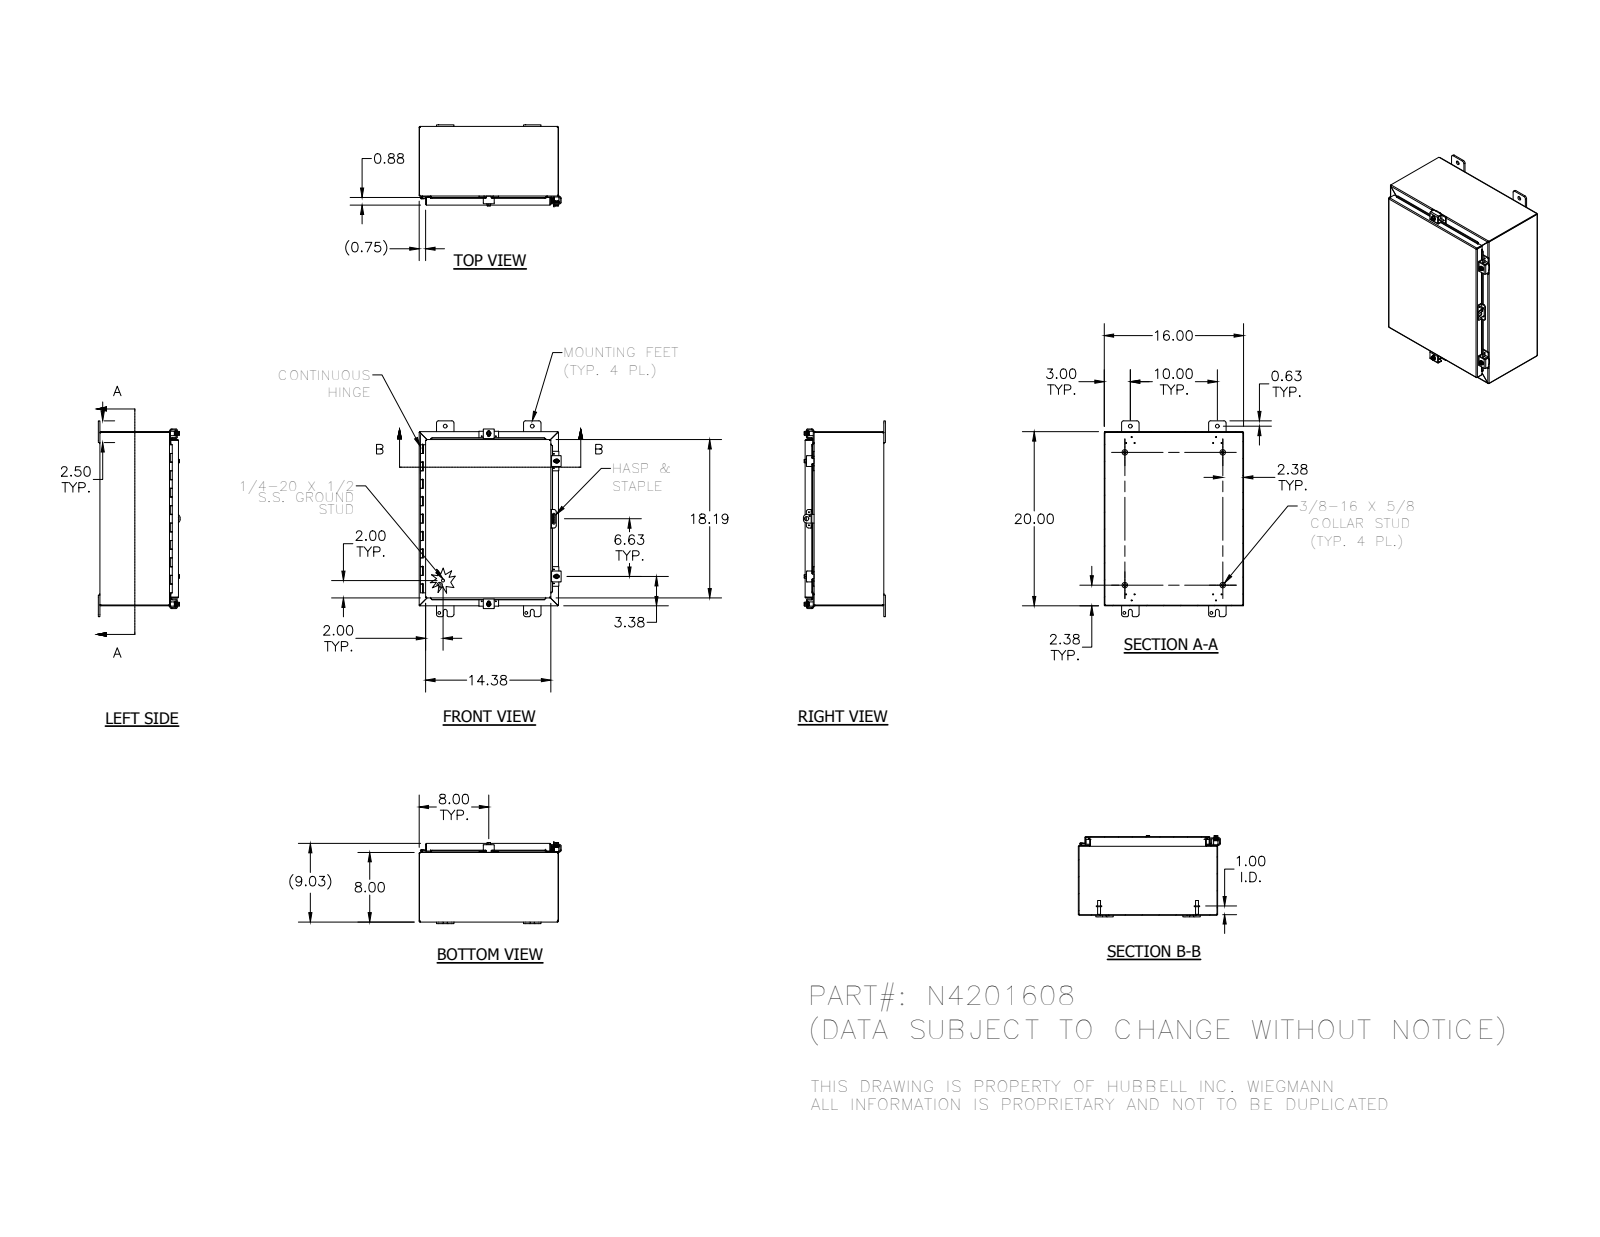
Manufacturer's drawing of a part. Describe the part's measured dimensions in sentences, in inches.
The part is named "HFW30825-3_1; 328104P-1_1; 34840_1; 38846_1 (+8 more)". Its 3-D file was written by "SolidWorks 2014 (AUTOMOTIVE_DESIGN)". It is 37 solids with 1614 faces: 633 planar, 724 cylindrical and 257 other. Overall it measures 22.5 by 16.311 by 9.41 inches. Its volume is 115.5 cubic inches and its surface area 2 996 square inches. Round holes: 12 of diameter 0.12, 11 of diameter 0.11, 4 of diameter 0.211, 4 of diameter 0.281, 4 of diameter 0.3, 4 of diameter 0.313, 4 of diameter 0.438, 1 of diameter 0.125, 1 of diameter 0.156, 1 of diameter 0.5. Round bosses or shafts: 6 of diameter 0.25, 4 of diameter 0.625, 4 of diameter 0.52, 4 of diameter 0.5, 4 of diameter 0.35, 4 of diameter 0.33, 2 of diameter 0.115, 1 of diameter 0.337. Partial cylindrical surfaces (rounded edges, fillets, slot ends): 49 of radius 0.03, 33 of radius 0.062, 33 of radius 0.125, 29 of radius 0.25, 23 of radius 0.031, 23 of radius 0.105, 8 of radius 0.07, 8 of radius 0.141. The main face-to-face distances are 0.074, 8.959, 15.926, 8.885, 9.033, 19.926, 7.926, 1.033, 15.852, 16. The hole center spacings are 10, 0.876, 19.294, 0.759, 0.839, 0.94, 0.969, 1.593.
